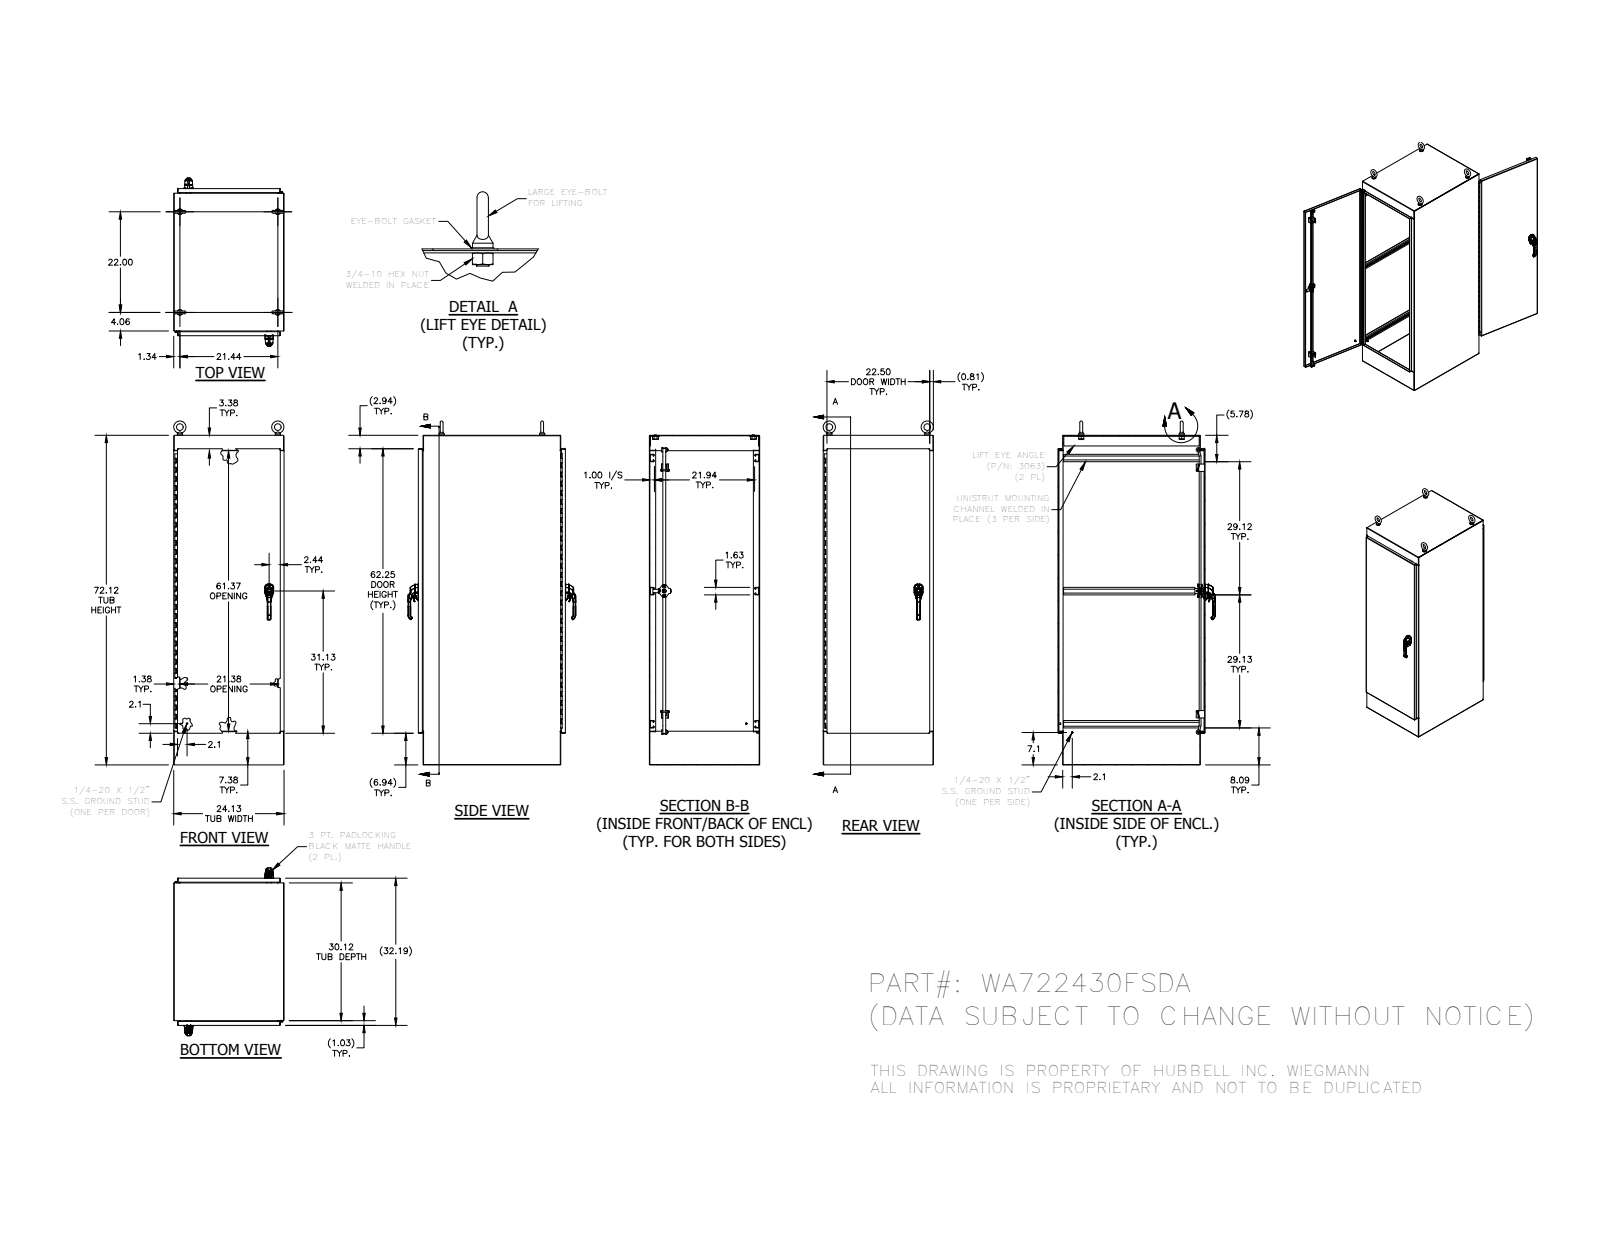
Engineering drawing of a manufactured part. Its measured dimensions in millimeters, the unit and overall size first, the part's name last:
Units: millimetres
Overall size (bounding box): 1911.29 × 932.81 × 612.77
Round holes (diameter × count): ⌀7.02 ×16, ⌀5.08 ×8, ⌀5.4 ×6, ⌀6 ×6, ⌀7.11 ×6, ⌀6.13 ×4, ⌀6.35 ×4, ⌀6.41 ×4, ⌀10.16 ×4, ⌀10.33 ×4, ⌀10.5 ×4, ⌀11.43 ×4
Round bosses / shafts (diameter × count): ⌀6.35 ×6, ⌀31.75 ×4, ⌀28.45 ×4, ⌀25.4 ×4, ⌀19.05 ×4, ⌀14.29 ×4, ⌀13.37 ×4, ⌀12.7 ×4
Partial cylindrical surfaces — rounded edges, fillets, slot ends (radius × count): R0.5 ×332, R0.3 ×169, R0.47 ×38, R0.25 ×32, R2 ×30, R1.27 ×28, R0.79 ×26, R3 ×24
Main face-to-face distances: 2.38, 610.4, 815.19, 608.02, 612.78, 1829.59, 812.81, 817.57, 26.3, 788.89
Hole centre spacings: 447.64, 9.66, 9.7, 9.71, 12.5, 19.36, 19.4, 22.5
Volume: 17 740 000 mm³ · Surface area: 15 070 000 mm²
Bodies: 90 solids, 5786 faces (2392 planar, 2036 cylindrical, 1358 other)
Part name (STEP PRODUCT): WA7230FSDALRS; WA2430FSDABTM; WA2430FSDATOP; WA7224FSDADR (+8 more)
STEP written by: Autodesk Inventor 2014 (AUTOMOTIVE_DESIGN)
